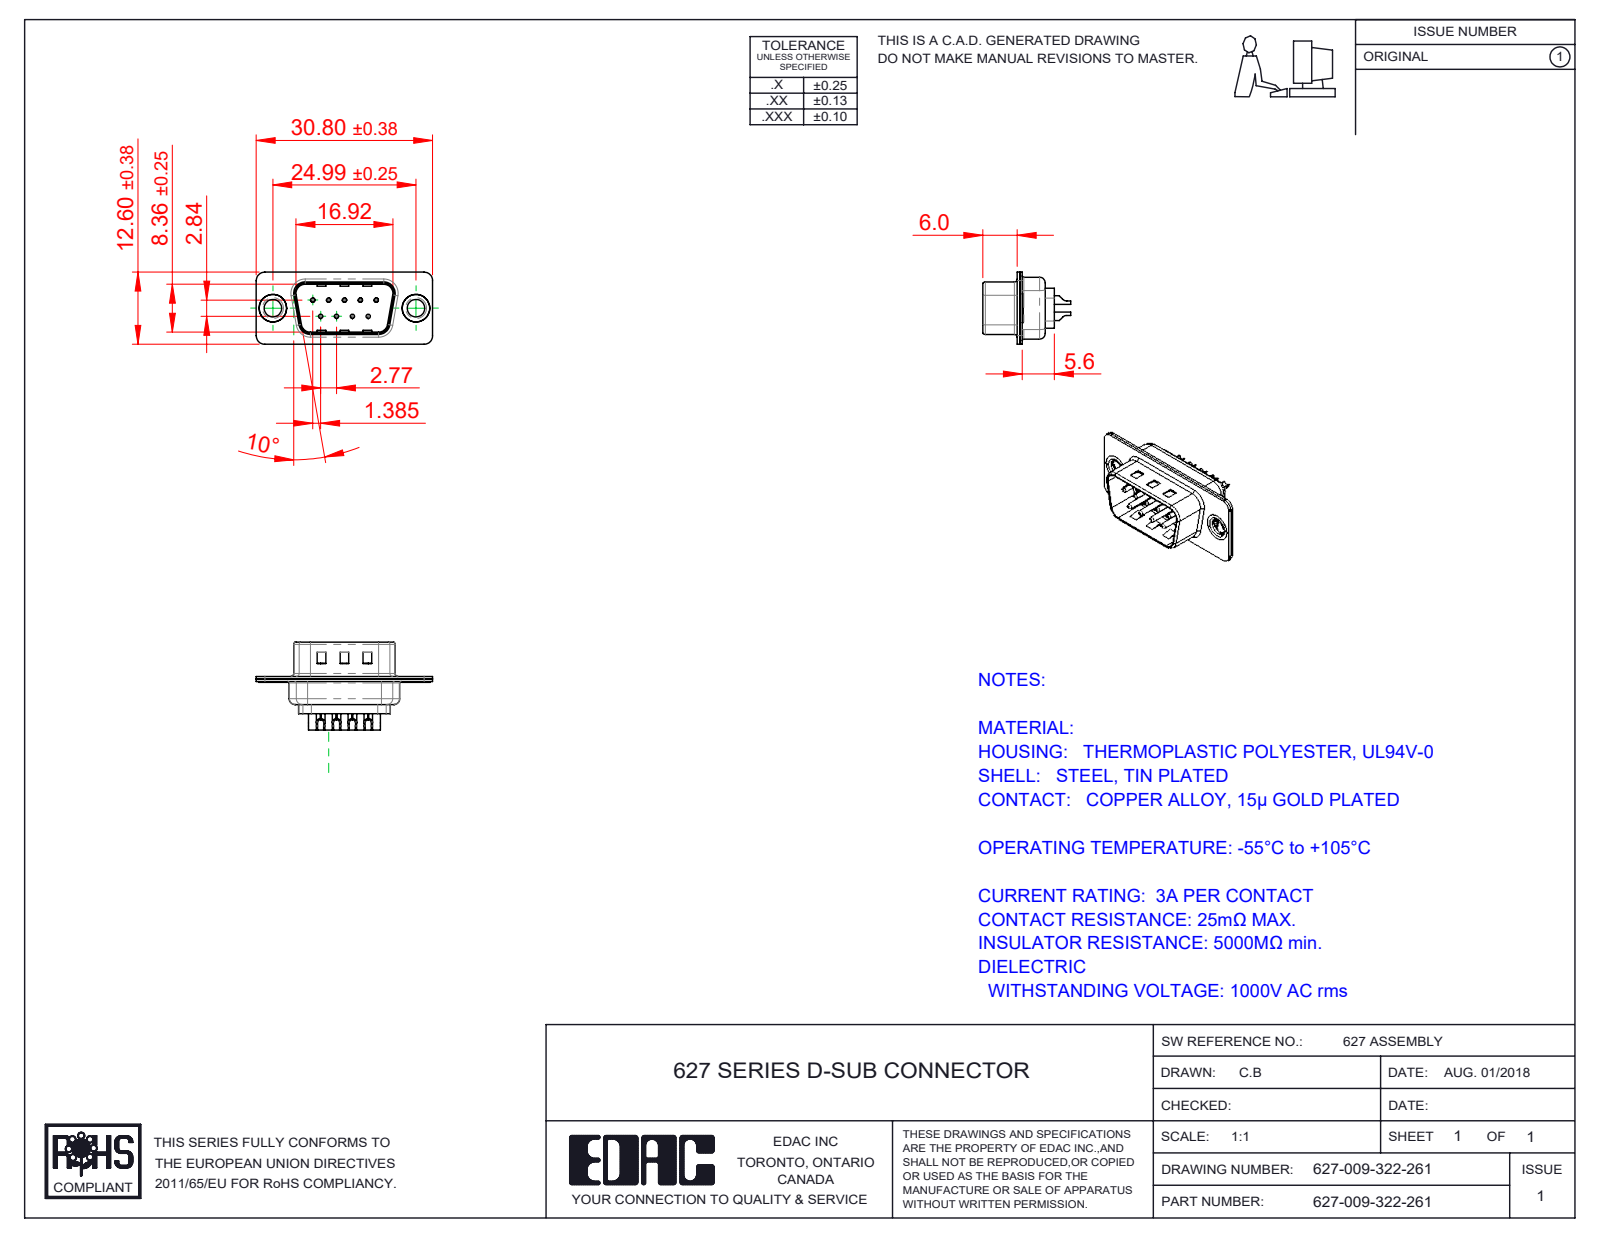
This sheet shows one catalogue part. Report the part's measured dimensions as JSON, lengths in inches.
{"part_name": "627 Thru Hole Rivet; 627 Shell Rear_09 Contacts; 627 Shell Front_09 Contacts; 627 Housing_09 LP (+3 more)", "step_written_by": "SolidWorks 2020 (CONFIG_CONTROL_DESIGN)", "units": "inches", "bodies": {"solids": 14, "faces": 854, "planar": 233, "cylindrical": 374, "other": 247}, "overall_size": [1.213, 0.604, 0.496], "volume_in3": 0.075, "surface_area_in2": 5.902, "round_holes": [[0.014, 9], [0.043, 9], [0.063, 9], [0.12, 2], [0.157, 2], [0.189, 2]], "round_bosses_or_shafts": [[0.079, 9], [0.059, 9], [0.03, 9], [0.197, 2], [0.193, 2], [0.14, 2]], "partial_cylinders_radius": [[0.059, 18], [0.079, 12], [0.02, 8], [0.063, 8], [0.039, 6], [0.01, 4], [0.024, 4], [0.026, 4]], "face_to_face_distances": [0.018, 0.016, 0.035, 0.032, 0.377, 0.055, 0.02, 0.345, 0.059, 0.256], "hole_center_spacings": [0.124, 0.109, 0.218, 0.198, 0.198, 0.327, 0.294, 0.295]}
